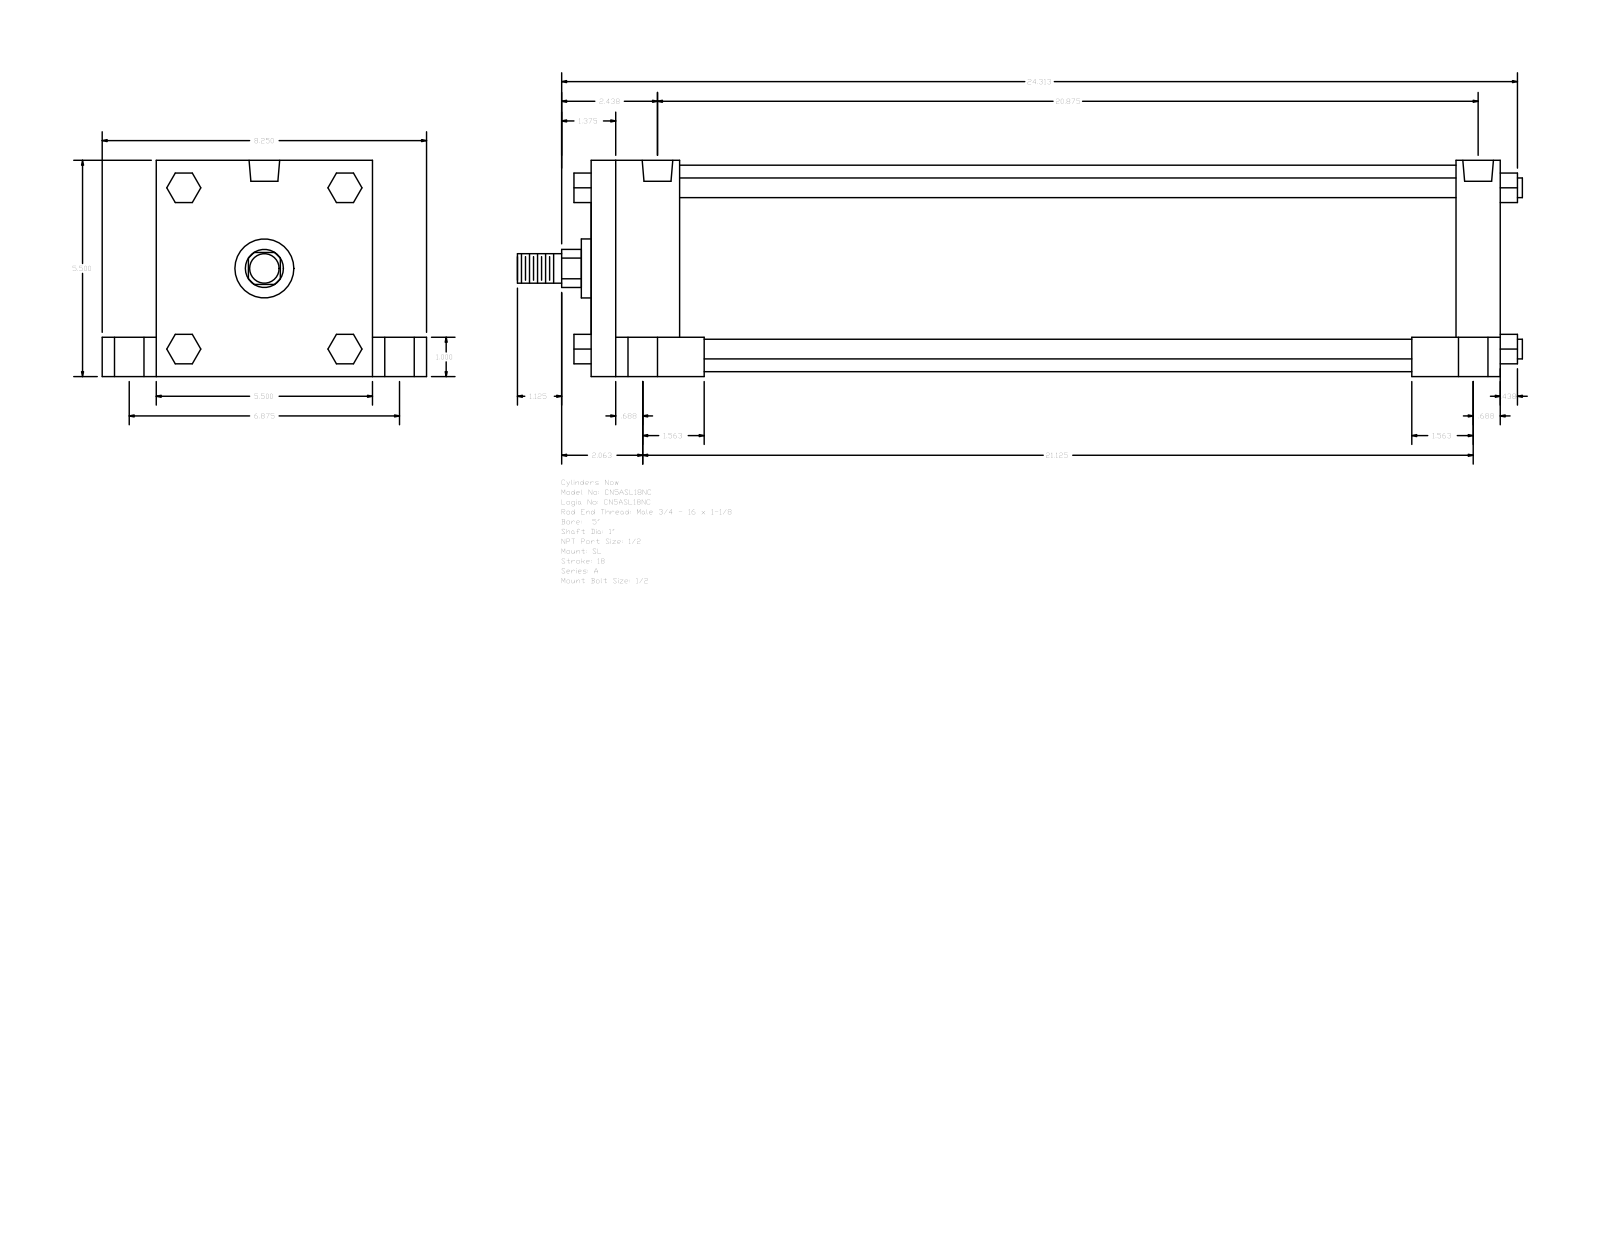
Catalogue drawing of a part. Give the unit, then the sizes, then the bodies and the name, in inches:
Units: inches
Overall size (bounding box): 25.563 × 8.25 × 5.5
Round holes (diameter × count): ⌀0.344 ×4, ⌀0.75 ×4, ⌀1 ×4, ⌀0.778 ×2
Round bosses / shafts (diameter × count): ⌀0.5 ×4, ⌀5.25 ×1, ⌀1.5 ×1, ⌀1 ×1, ⌀0.75 ×1
Partial cylindrical surfaces — rounded edges, fillets, slot ends (radius × count): R0.484 ×1
Main face-to-face distances: 5.5, 23.125, 2.25, 20.875, 1, 4.5, 1.375, 6.875, 1.125, 22
Hole centre spacings: 0.094, 3.437, 3.44, 3.458, 3.469, 6.875, 20.687, 20.781
Bodies: 0 solids, 150 faces (114 planar, 36 cylindrical, 0 other)
Part name (STEP PRODUCT): A_SL__0500_1
STEP written by: GSSL Pune (CONFIG_CONTROL_DESIGN)
